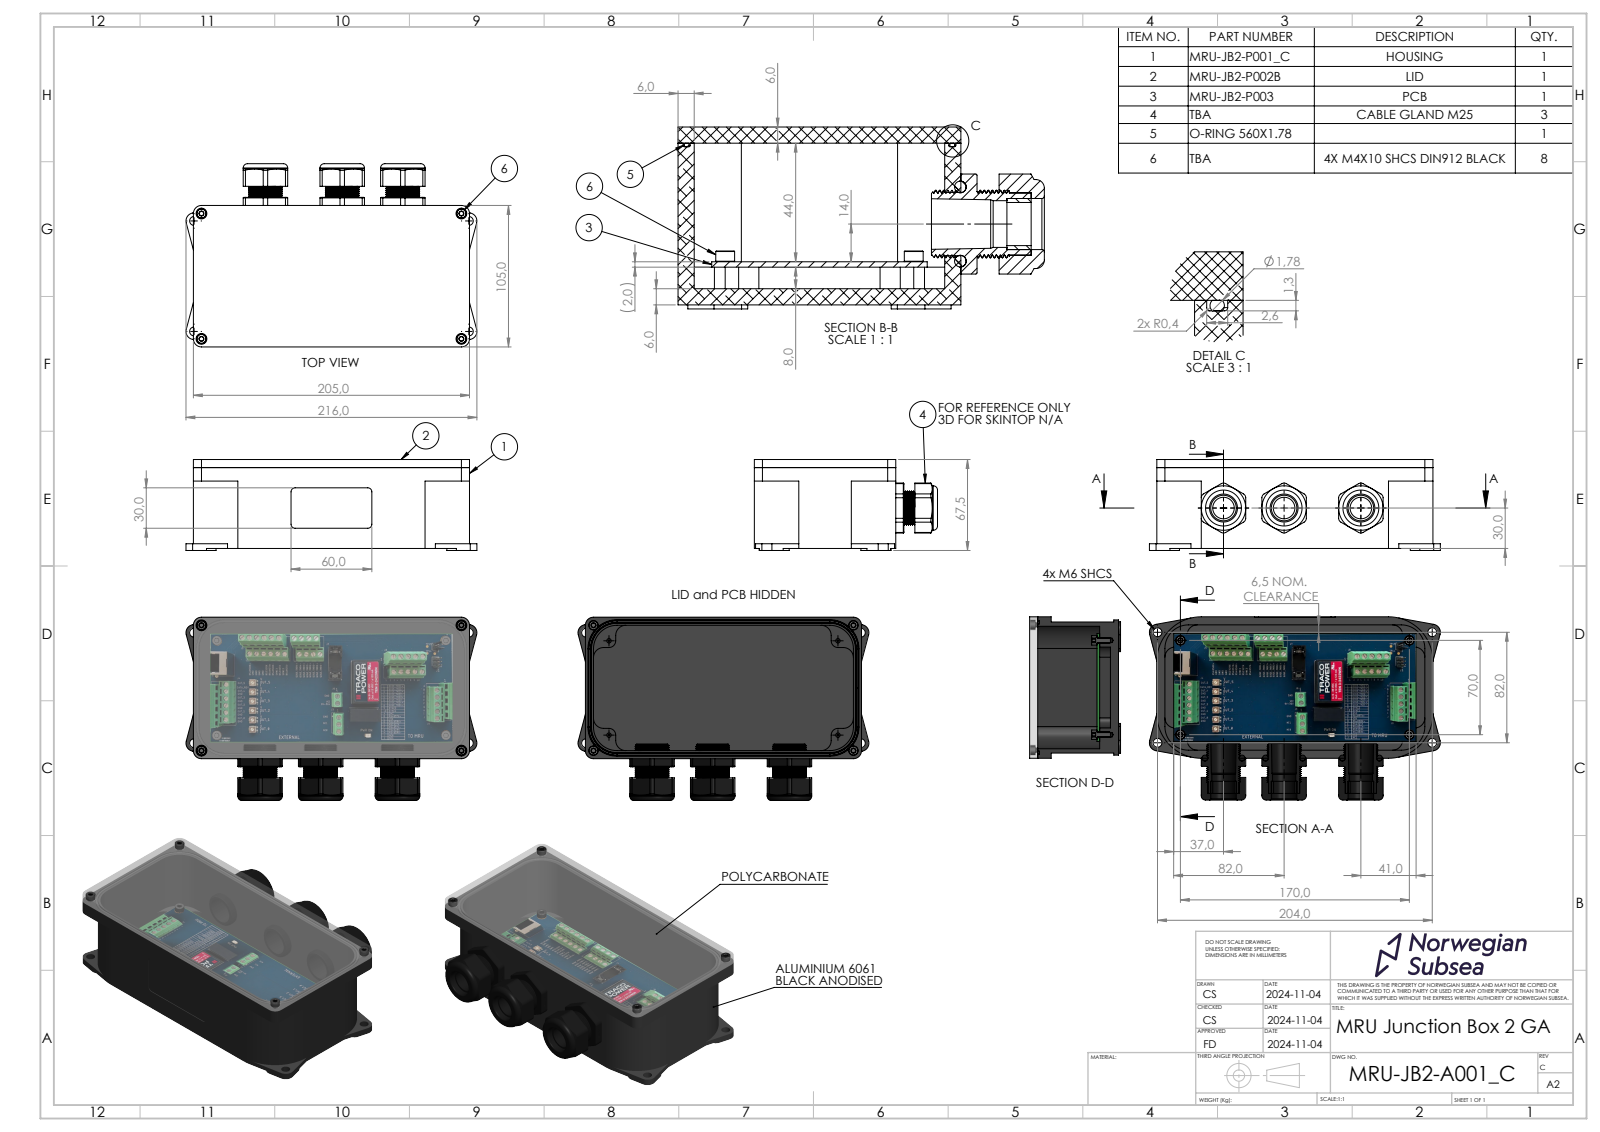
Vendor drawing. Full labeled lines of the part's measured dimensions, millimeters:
Part name (STEP PRODUCT): MRU-JB2-A001_C; MRU-JB2-P003; MRU-JB2-P002B; M4x10 SHCS DIN912_91290A144 (+3 more)
STEP written by: SolidWorks 2024 (AUTOMOTIVE_DESIGN)
Units: millimetres
Bodies: 24 solids, 1419 faces (455 planar, 550 cylindrical, 414 other)
Overall size (bounding box): 216 × 135.99 × 67.5
Volume: 508 889 mm³ · Surface area: 236 402 mm²
Round holes (diameter × count): ⌀3.3 ×8, ⌀4.3 ×4, ⌀4.5 ×4, ⌀6.6 ×4, ⌀8 ×4, ⌀16 ×3, ⌀17.34 ×3, ⌀18.95 ×3, ⌀23.1 ×3, ⌀23.5 ×3
Round bosses / shafts (diameter × count): ⌀7 ×8, ⌀4 ×8, ⌀33.02 ×3, ⌀25 ×3
Partial cylindrical surfaces — rounded edges, fillets, slot ends (radius × count): R3.3 ×18, R6 ×16, R0.4 ×8, R7.5 ×8, R0.89 ×4, R3 ×4, R5 ×4, R17.5 ×4
Main face-to-face distances: 6, 60, 66, 54, 8, 99, 10, 14, 50, 46
Hole centre spacings: 7.78, 16.26, 18.03, 77.88, 82.31, 87.67, 181.86, 187.1
